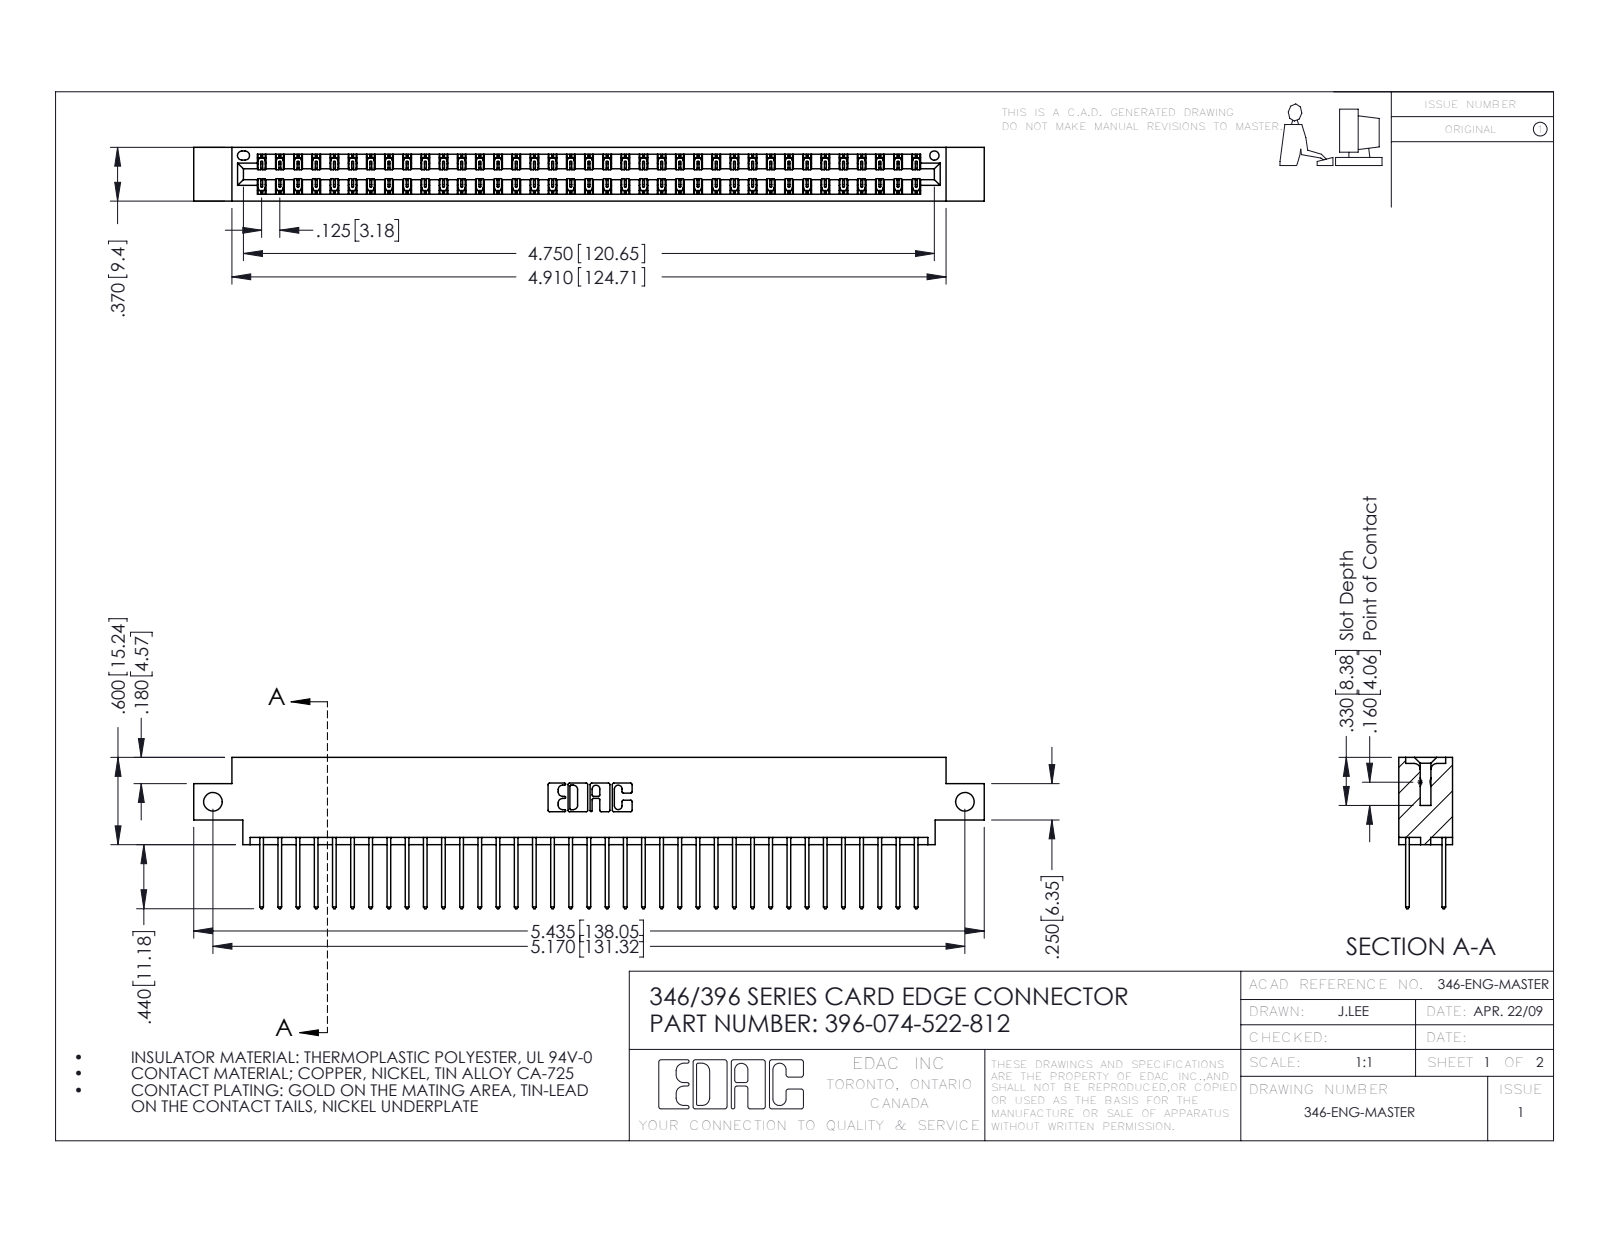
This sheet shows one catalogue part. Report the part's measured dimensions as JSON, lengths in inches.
{"part_name": "345-292-001_345-293-122; 346 Part_0.170 Offset - Side Mount; 396-074-522-812", "step_written_by": "SolidWorks 2016 (CONFIG_CONTROL_DESIGN)", "units": "inches", "bodies": {"solids": 75, "faces": 3974, "planar": 2670, "cylindrical": 1304, "other": 0}, "overall_size": [5.435, 1.04, 0.37], "volume_in3": 0.816, "surface_area_in2": 29.79, "round_holes": [[0.128, 2], [0.064, 1]], "partial_cylinders_radius": [[0.006, 111], [0.01, 74], [0.01, 22], [0.007, 6], [0.031, 6], [0.026, 3], [0.014, 2], [0.022, 2]], "face_to_face_distances": [0.048, 0.322, 0.25, 0.37, 0.072, 0.298, 0.025, 0.275, 0.148, 0.222], "hole_center_spacings": [5.17]}
